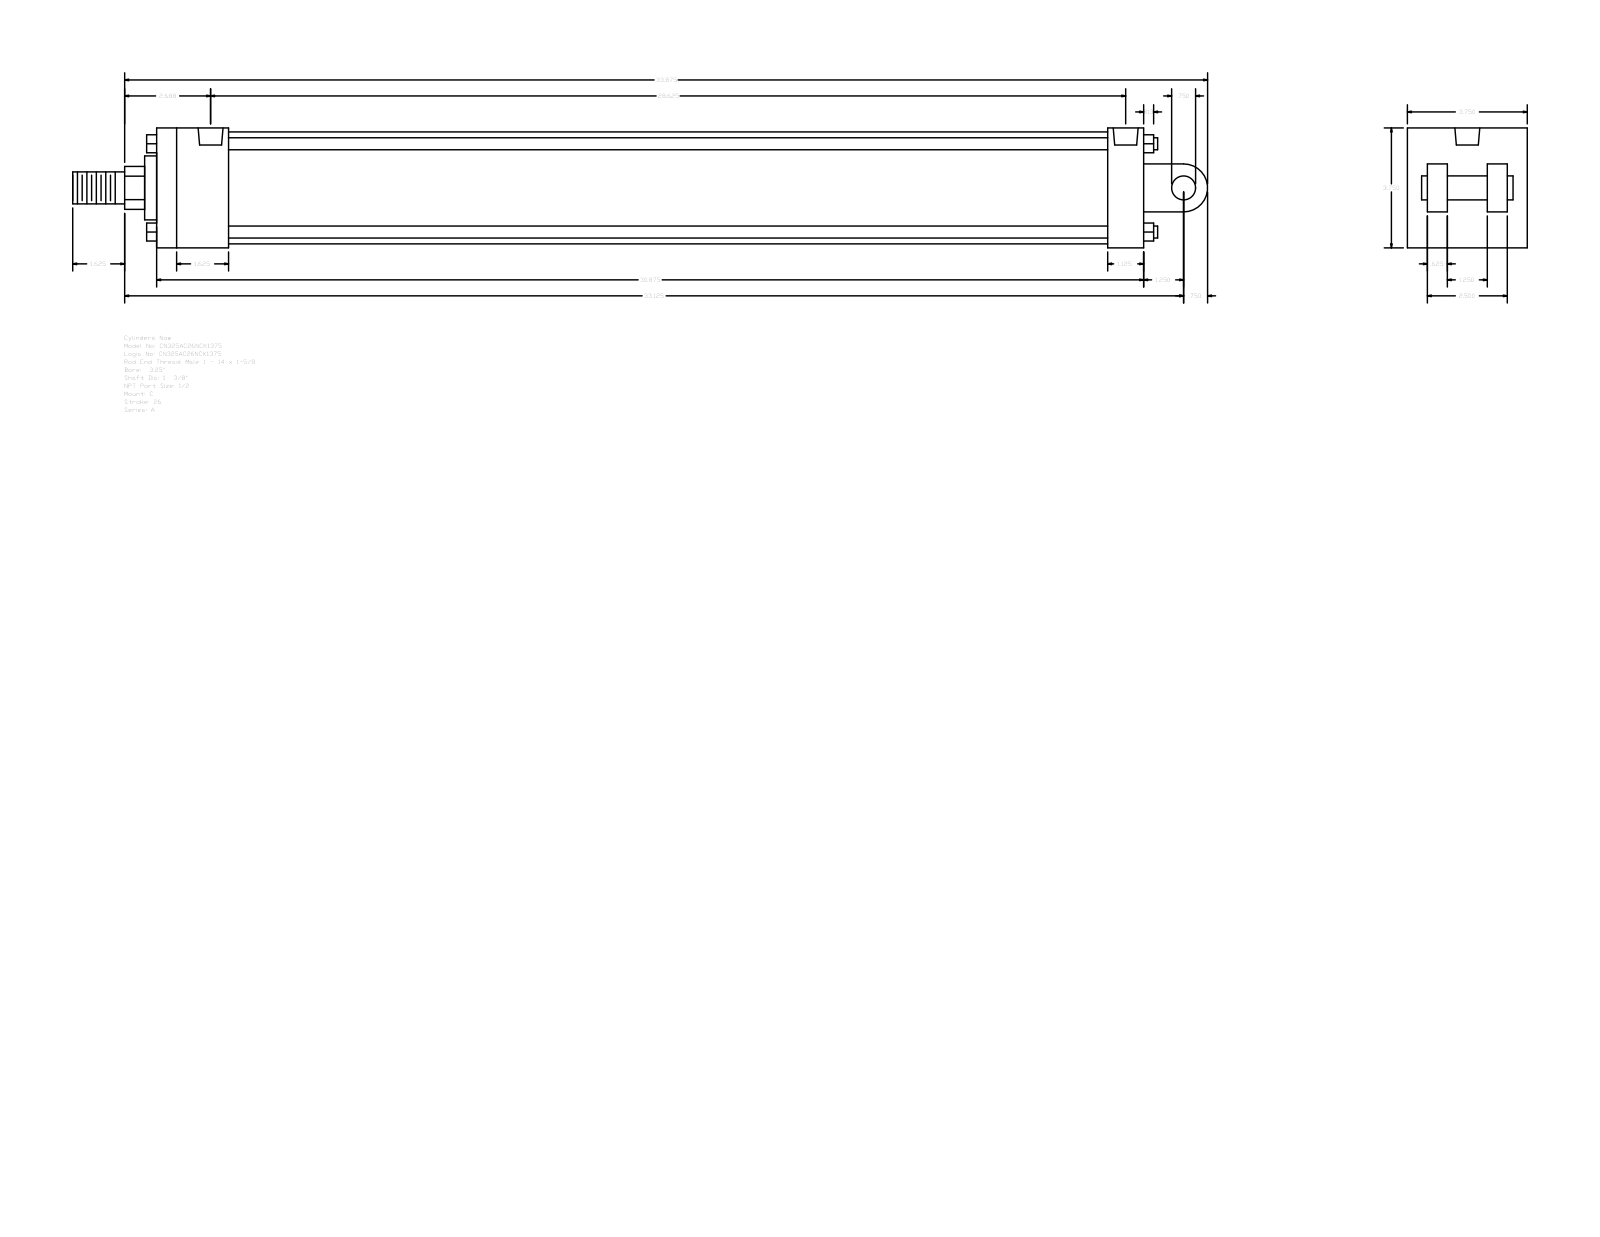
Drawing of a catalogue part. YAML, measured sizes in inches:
part_name: "A_C__0325_1.375"
step_written_by: "GSSL Pune (CONFIG_CONTROL_DESIGN)"
units: inches
bodies: {solids: 0, faces: 135, planar: 102, cylindrical: 33, other: 0}
overall_size: [35.5, 3.75, 3.75]
round_holes:
  - {diameter: 0.344, count: 4}
  - {diameter: 0.778, count: 2}
round_bosses_or_shafts:
  - {diameter: 0.375, count: 4}
  - {diameter: 3.5, count: 1}
  - {diameter: 2, count: 1}
  - {diameter: 1.375, count: 1}
  - {diameter: 1, count: 1}
  - {diameter: 0.75, count: 1}
partial_cylinders:
  - {radius: 0.672, count: 1}
  - {radius: 0.75, count: 1}
face_to_face_distances: [3.75, 30.875, 0.625, 1.125, 2.5, 2.625, 2.25, 1.25, 3.125, 1.875]
hole_center_spacings: [0.125, 28.375, 28.5, 28.625]
